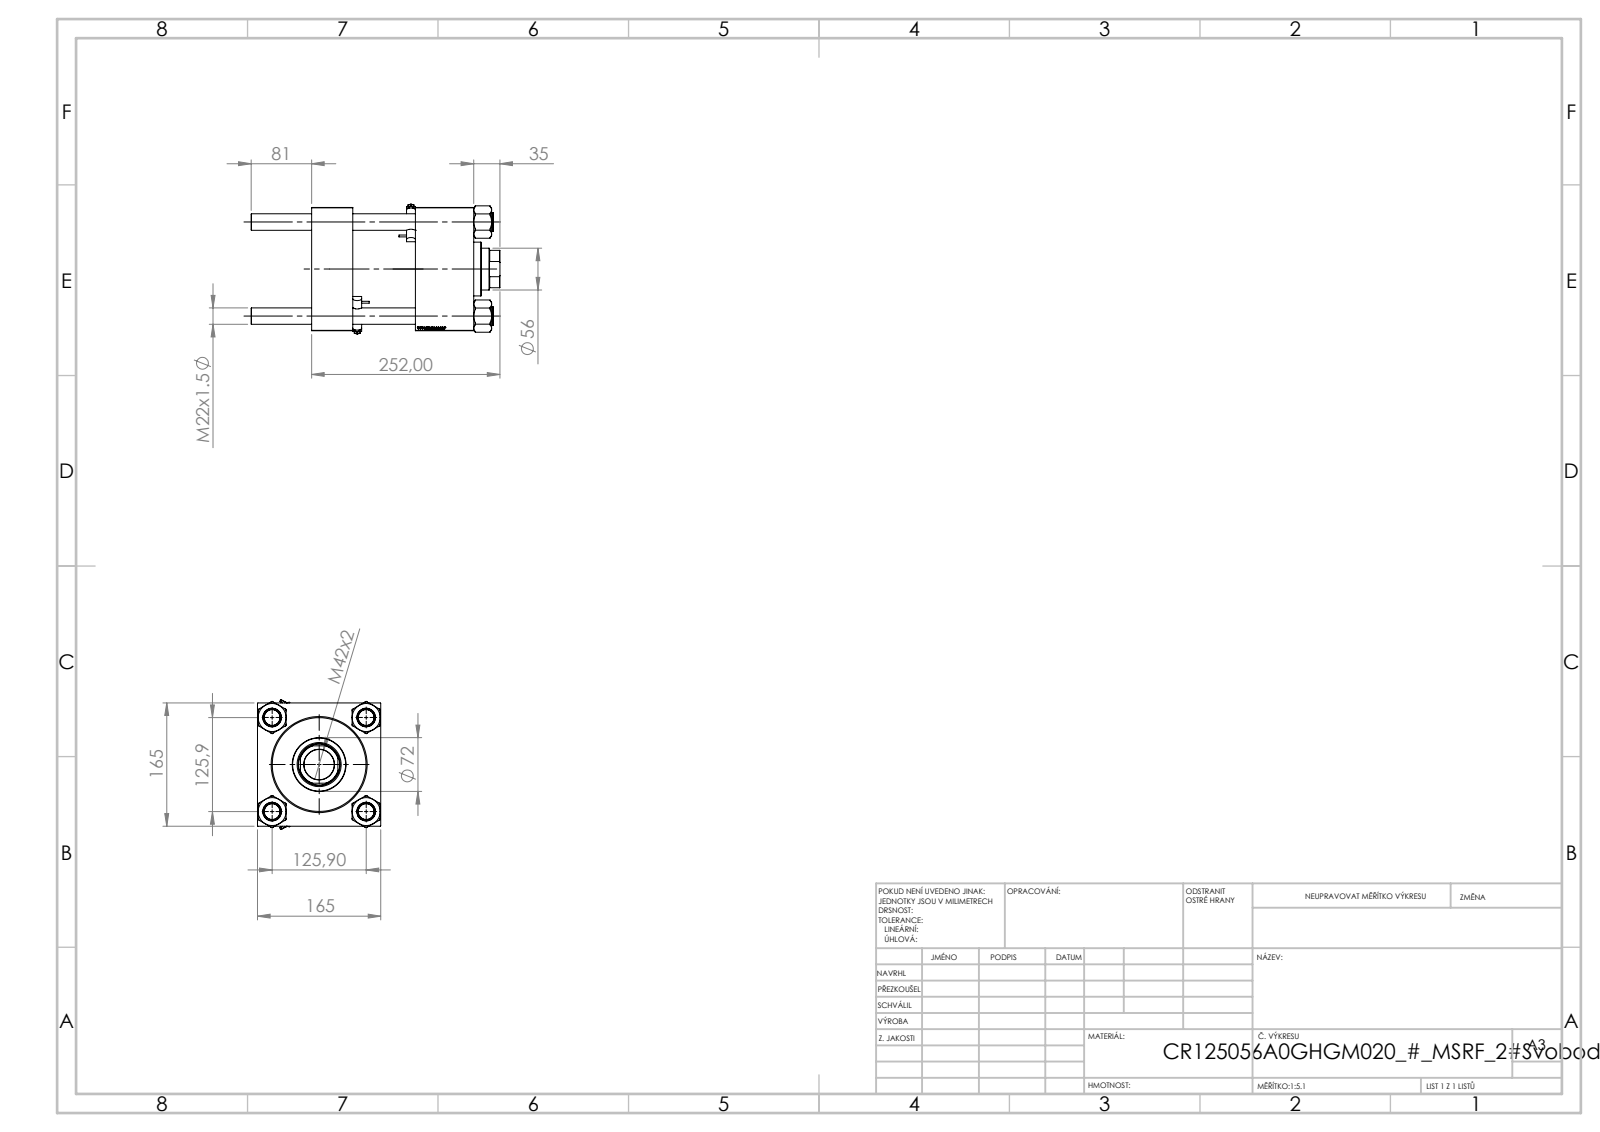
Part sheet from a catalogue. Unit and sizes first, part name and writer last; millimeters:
Units: millimetres
Overall size (bounding box): 333 × 173.85 × 165
Round holes (diameter × count): ⌀22 ×4, ⌀7 ×2, ⌀32.24 ×2, ⌀45 ×2, ⌀40.5 ×1, ⌀56 ×1, ⌀59 ×1, ⌀96 ×1, ⌀125 ×1, ⌀125.5 ×1
Round bosses / shafts (diameter × count): ⌀25 ×4, ⌀5 ×2, ⌀2.5 ×2, ⌀131 ×1, ⌀72 ×1
Partial cylindrical surfaces — rounded edges, fillets, slot ends (radius × count): R0.5 ×12, R6 ×4, R27 ×1
Main face-to-face distances: 165, 55, 162, 217, 139, 84, 78, 188.3, 133.3, 49.3
Hole centre spacings: 89.02, 125.9, 178.05, 138.5
Volume: 4 689 000 mm³ · Surface area: 553 706 mm²
Bodies: 13 solids, 1246 faces (604 planar, 106 cylindrical, 536 other)
Part name (STEP PRODUCT): MSRF_MSRG1; CR025_012_A_0_G_A_G_M_020_+#_##_TYCINKA; NUT_M5; V215CR_VCP (+2 more)
STEP written by: SolidWorks 2019 (CONFIG_CONTROL_DESIGN)
